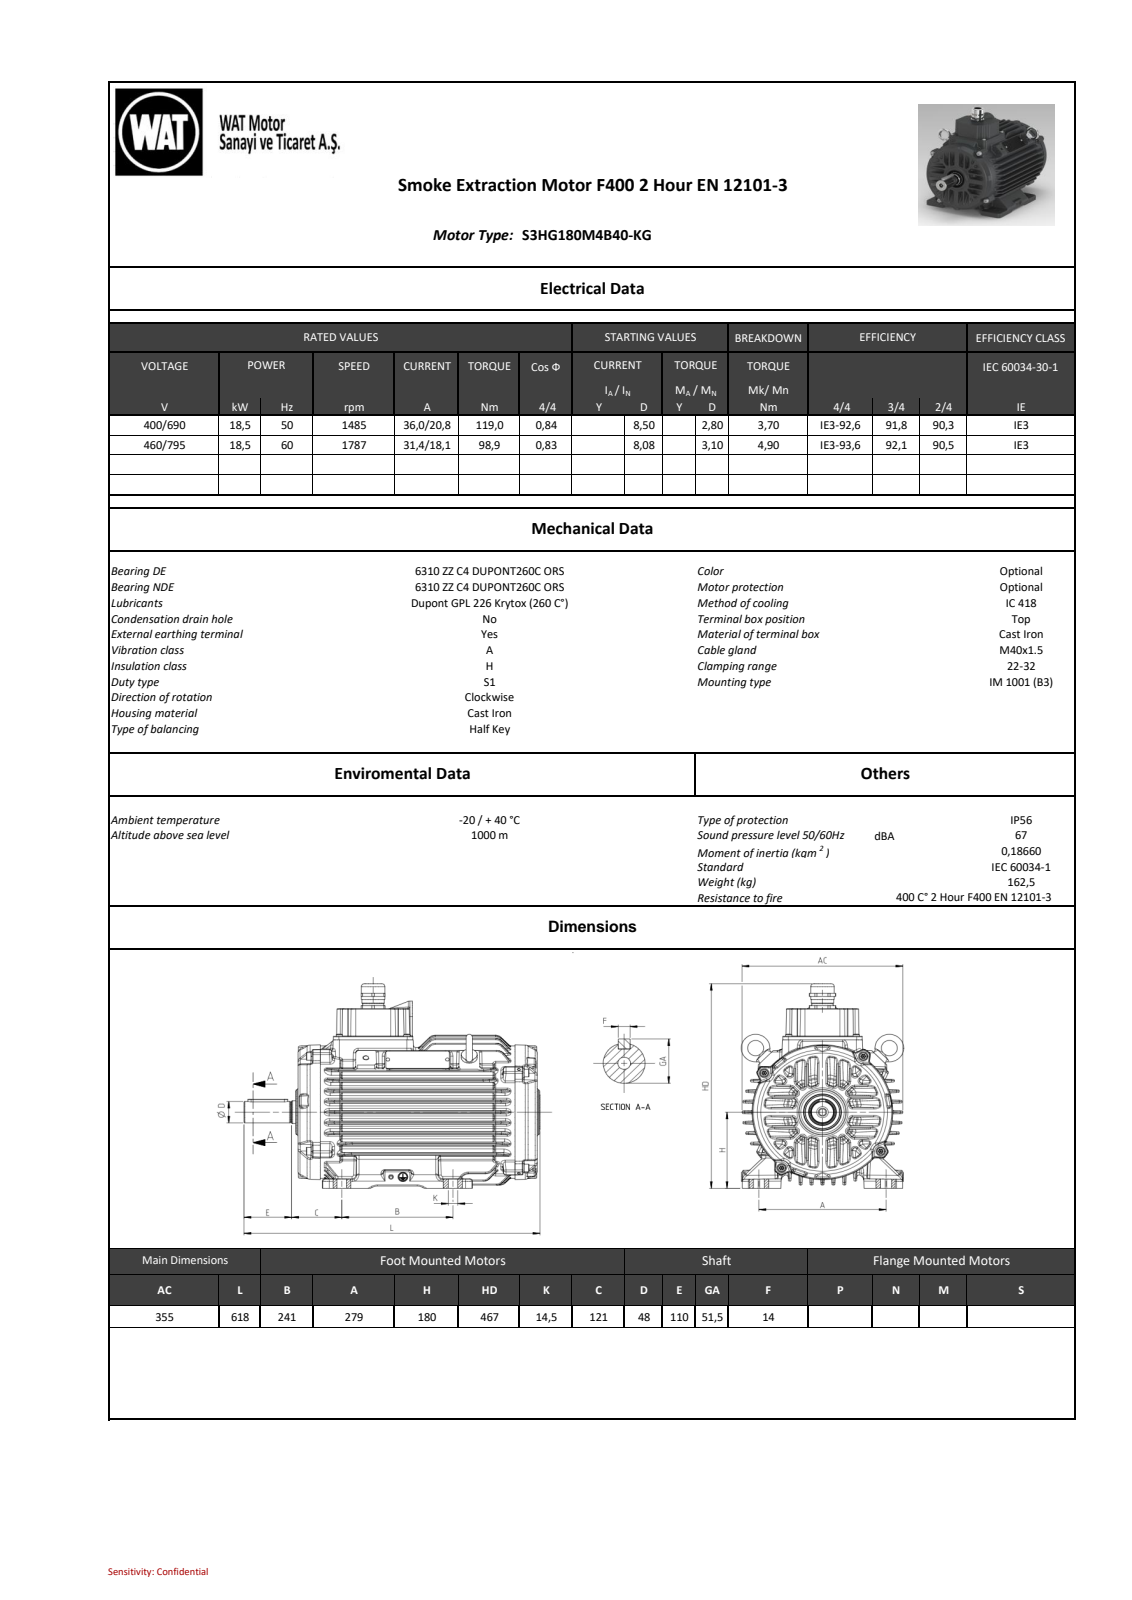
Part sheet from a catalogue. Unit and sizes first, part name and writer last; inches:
Units: inches
Overall size (bounding box): 24.331 × 18.386 × 13.987
Round holes (diameter × count): ⌀0.354 ×8, ⌀0.197 ×4, ⌀0.098 ×2, ⌀0.429 ×2, ⌀0.268 ×1, ⌀0.551 ×1, ⌀0.669 ×1, ⌀1.26 ×1, ⌀2.441 ×1, ⌀2.984 ×1, ⌀2.992 ×1
Round bosses / shafts (diameter × count): ⌀0.787 ×4, ⌀0.63 ×4, ⌀0.619 ×4, ⌀0.472 ×4, ⌀0.713 ×3, ⌀1.181 ×2, ⌀12.205 ×1, ⌀1.969 ×1
Partial cylindrical surfaces — rounded edges, fillets, slot ends (radius × count): R0.157 ×391, R0.118 ×172, R0.059 ×136, R0.079 ×86, R0.197 ×82, R0.071 ×64, R0.016 ×32, R0.394 ×20
Main face-to-face distances: 0.572, 1.147, 0.575, 2.311, 0.569, 1.142, 1.717, 1.724, 1.152, 0.577
Hole centre spacings: 8.797, 2.154, 6.22, 6.221, 7.142, 10.187, 12.254, 12.441
Bodies: 0 solids, 6895 faces (934 planar, 1617 cylindrical, 4344 other)
Part name (STEP PRODUCT): 26032C0836B7xjw5
STEP written by: SIEMENS PLM Software NX 11.0 (AUTOMOTIVE_DESIGN)
